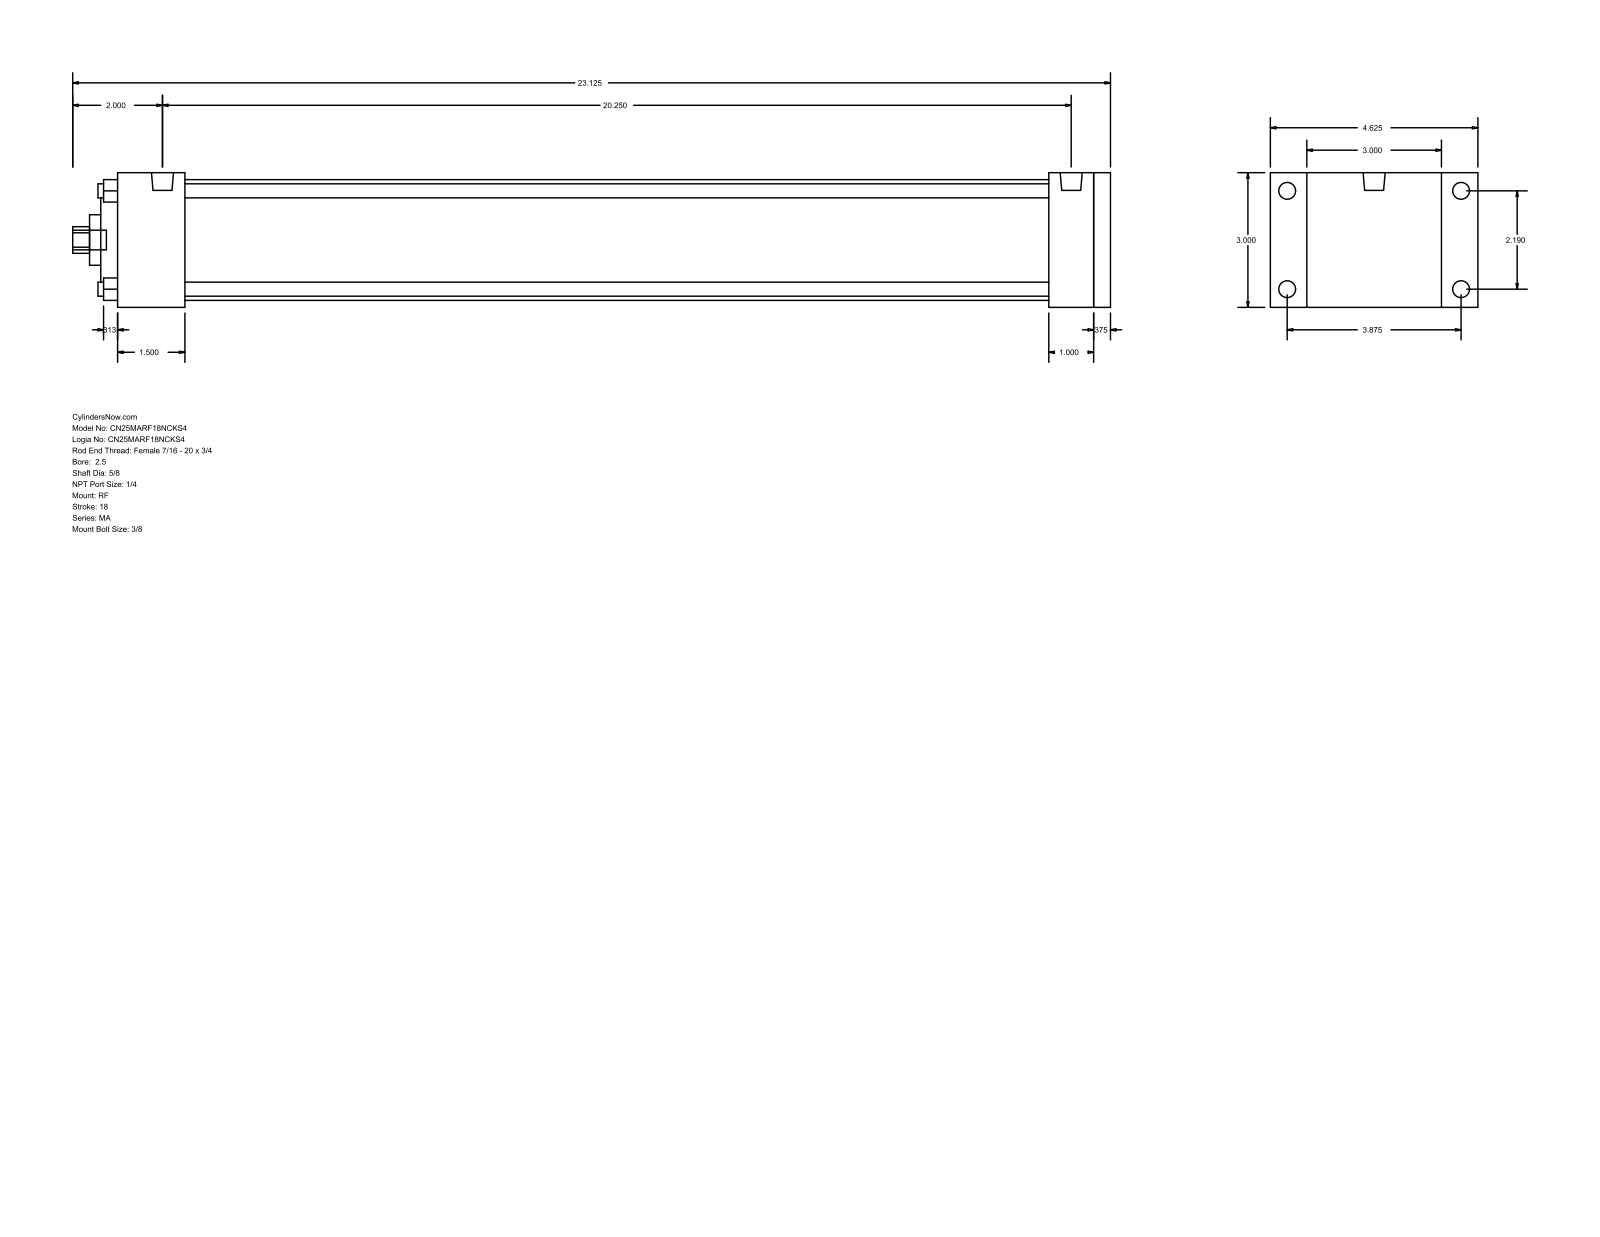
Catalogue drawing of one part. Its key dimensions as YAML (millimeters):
part_name: "MA_RF__0250_0.625"
step_written_by: "GSSL Pune (CONFIG_CONTROL_DESIGN)"
units: millimeters
bodies: {solids: 0, faces: 94, planar: 65, cylindrical: 29, other: 0}
overall_size: [587.38, 117.47, 76.2]
round_holes:
  - {diameter: 7.94, count: 4}
  - {diameter: 15.88, count: 1}
  - {diameter: 28.57, count: 1}
  - {diameter: 50.8, count: 1}
  - {diameter: 68.33, count: 1}
round_bosses_or_shafts:
  - {diameter: 9.53, count: 4}
  - {diameter: 7.94, count: 4}
  - {diameter: 12.49, count: 2}
  - {diameter: 11.11, count: 1}
partial_cylinders:
  - {radius: 7.54, count: 1}
face_to_face_distances: [76.2, 561.98, 9.53, 552.45, 25.4, 38.1, 527.05, 488.95, 514.35, 523.88]
hole_center_spacings: [39.33, 55.62, 78.66]
